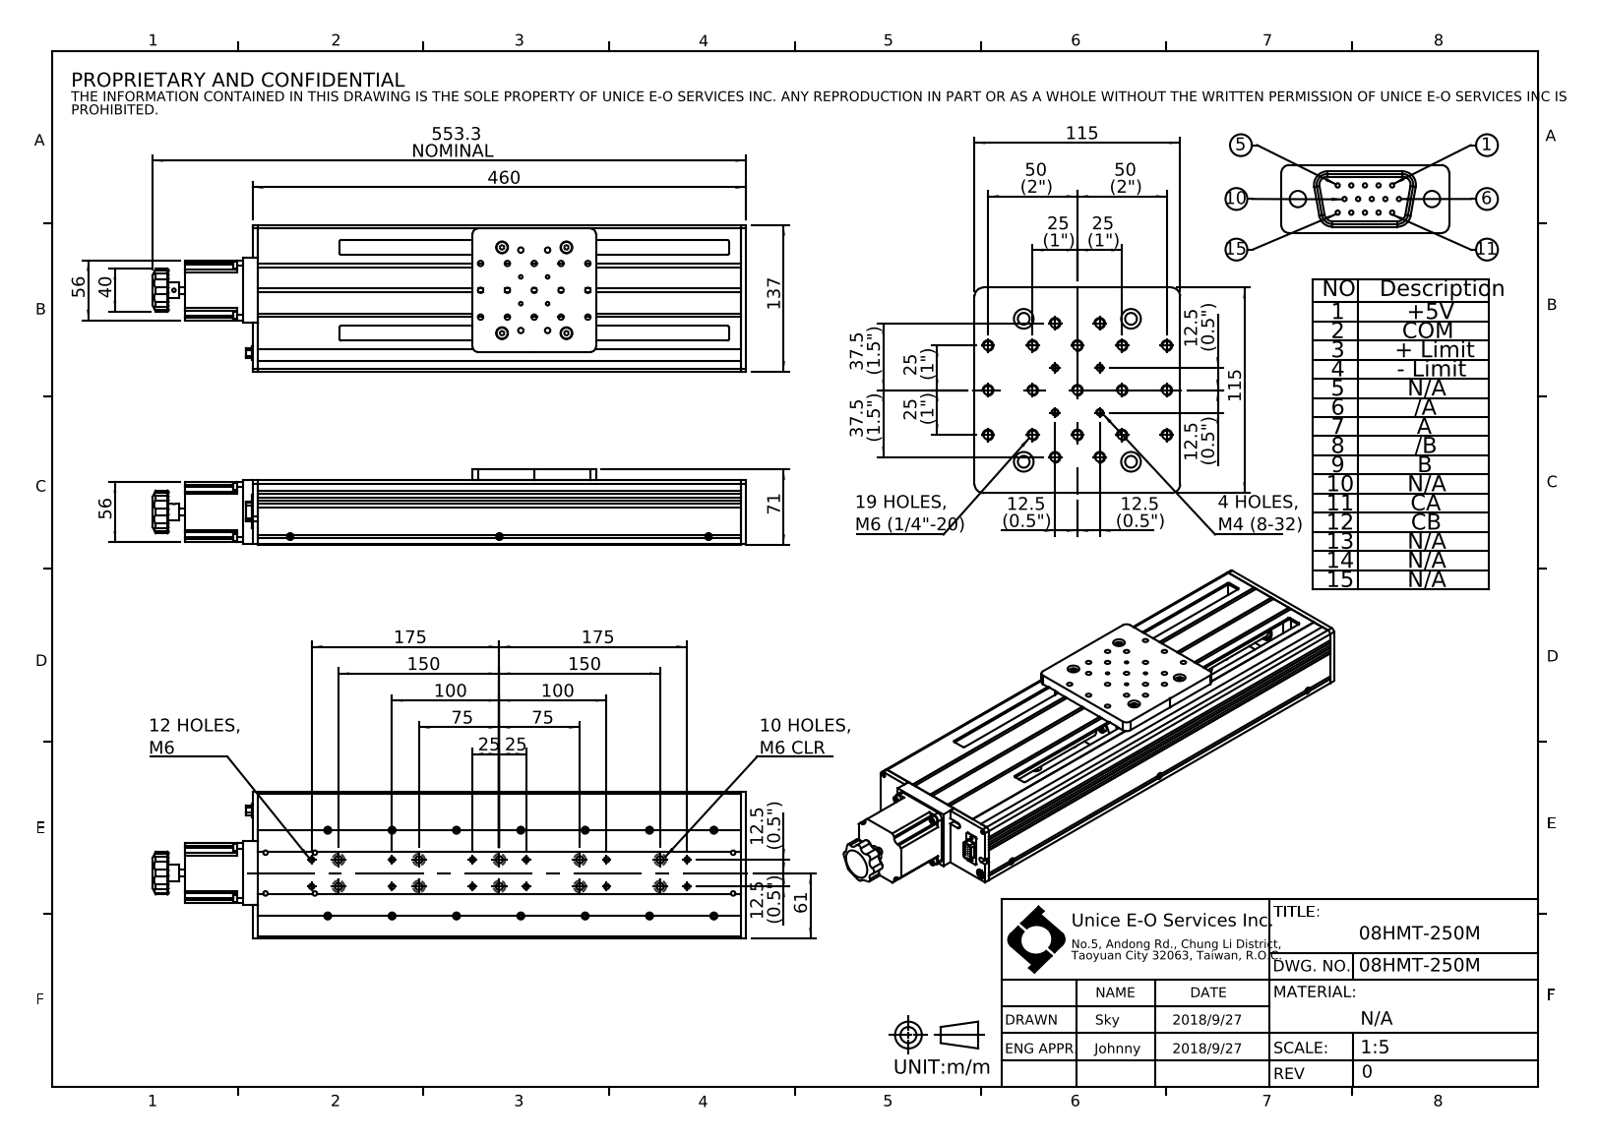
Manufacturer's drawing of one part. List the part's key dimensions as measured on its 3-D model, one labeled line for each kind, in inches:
Part name (STEP PRODUCT): 08HMT-250M
STEP written by: SolidWorks 2016 (AUTOMOTIVE_DESIGN)
Units: inches
Bodies: 0 solids, 807 faces (371 planar, 323 cylindrical, 113 other)
Overall size (bounding box): 21.783 × 5.394 × 2.795
Round holes (diameter × count): ⌀0.197 ×31, ⌀0.256 ×14, ⌀0.031 ×13, ⌀0.433 ×13, ⌀0.26 ×10, ⌀0.13 ×6, ⌀0.165 ×6, ⌀0.079 ×2, ⌀0.089 ×2, ⌀0.12 ×2, ⌀0.866 ×1, ⌀0.984 ×1
Round bosses / shafts (diameter × count): ⌀0.256 ×4, ⌀0.228 ×3, ⌀0.303 ×2, ⌀0.276 ×2, ⌀0.591 ×1, ⌀0.551 ×1, ⌀0.25 ×1
Partial cylindrical surfaces — rounded edges, fillets, slot ends (radius × count): R0.059 ×12, R0.02 ×8, R0.157 ×8, R0.197 ×8, R0.292 ×8, R0.079 ×4, R0.177 ×4, R0.118 ×3
Main face-to-face distances: 0.079, 2.382, 5.315, 5.236, 0.413, 0.059, 2.323, 5.394, 0.067, 0.354
Hole centre spacings: 1.556, 0.984, 0.696, 2.201, 1.392, 1.969, 2.509, 2.088
